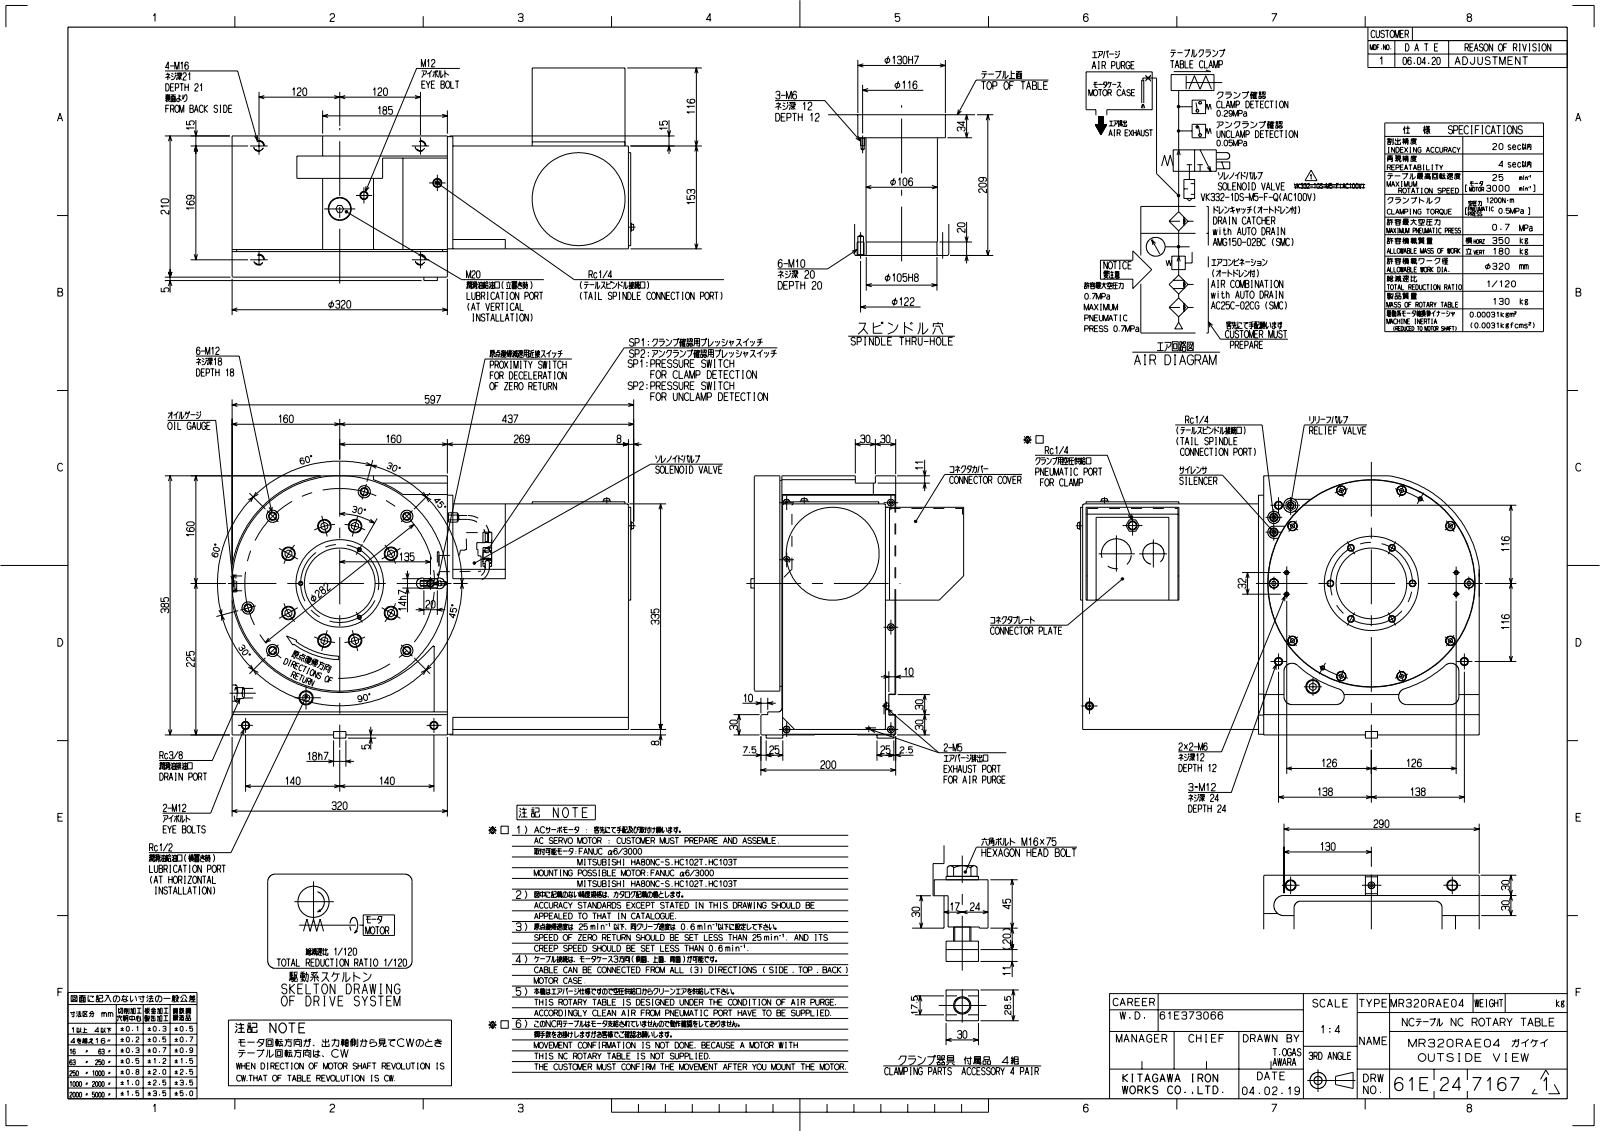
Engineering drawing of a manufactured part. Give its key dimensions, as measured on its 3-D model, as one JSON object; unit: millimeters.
{"step_written_by": "Unknown (AUTOMOTIVE_DESIGN)", "units": "millimeters", "bodies": {"solids": 1, "faces": 918, "planar": 621, "cylindrical": 239, "other": 58}, "overall_size": [596.7, 416, 342], "volume_mm3": 21080000, "surface_area_mm2": 1553000, "round_holes": [[5, 43], [6, 27], [14, 15], [10.2, 10], [12, 10], [16, 10], [20, 8], [7, 6], [108, 3], [9, 1], [9.73, 1], [10.7, 1]], "round_bosses_or_shafts": [[12, 9], [9, 9], [10, 6], [30, 4], [138, 2], [320, 1], [306, 1], [228, 1]], "partial_cylinders_radius": [[10, 10], [2, 9], [12, 6], [20, 4], [6, 2], [9, 1], [15, 1], [162, 1]], "face_to_face_distances": [2.3, 150.7, 42, 153, 44.3, 148.4, 192.7, 195, 8, 332.7], "hole_center_spacings": [45.16, 59, 83.44, 109.02, 45.15, 83.42, 108.99, 61]}
